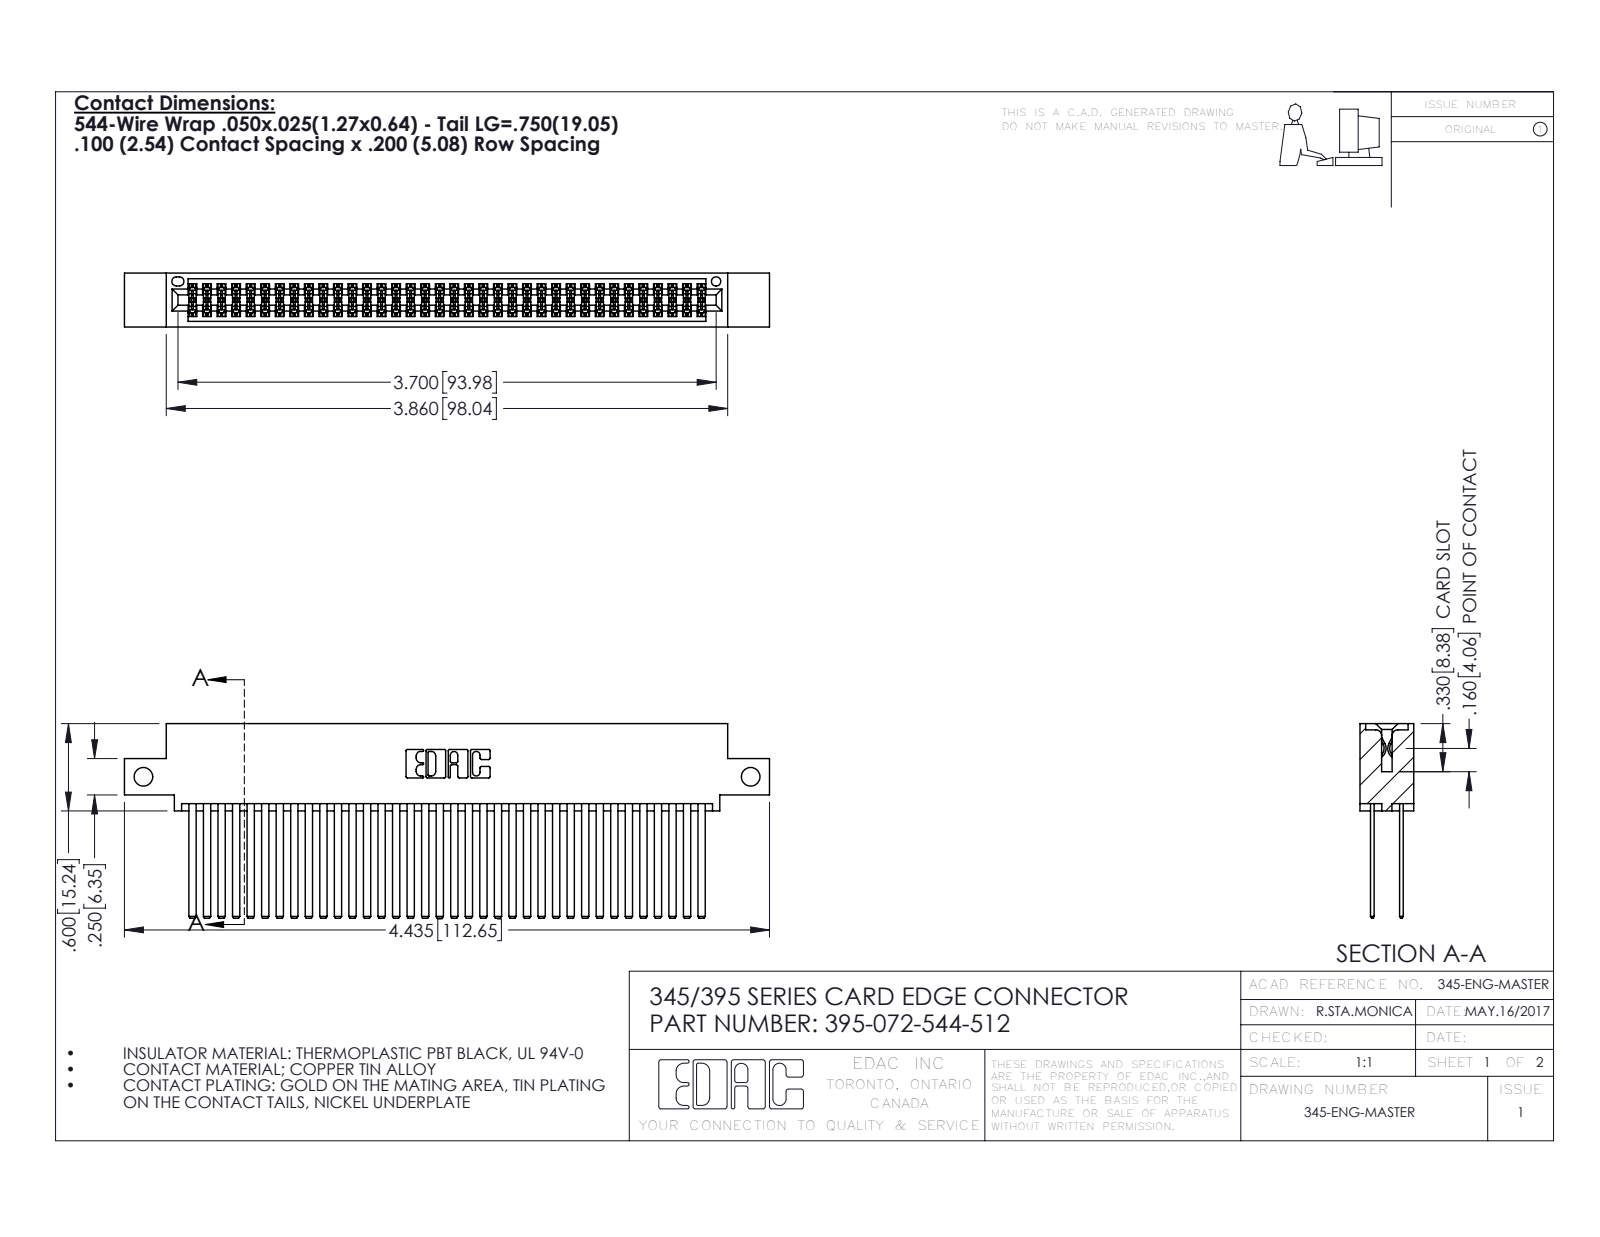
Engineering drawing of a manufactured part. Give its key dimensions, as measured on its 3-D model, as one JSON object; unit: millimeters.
{"part_name": "345 Part_0.110 Offset - Side Mount; 345-292-001_345-293-144; 395-072-544-512", "step_written_by": "SolidWorks 2016 (CONFIG_CONTROL_DESIGN)", "units": "millimeters", "bodies": {"solids": 73, "faces": 3298, "planar": 2172, "cylindrical": 1126, "other": 0}, "overall_size": [112.6, 34, 9.4], "volume_mm3": 11700, "surface_area_mm2": 20150, "round_holes": [[3.3, 2], [1.6, 1]], "partial_cylinders_radius": [[0.2, 108], [0.3, 22], [0.2, 6], [0.8, 6], [0.7, 3], [0.4, 2], [0.5, 2], [0.6, 2]], "face_to_face_distances": [5.1, 0.6, 7.6, 1.8, 2.5, 6.9, 5.7, 4.4, 9.4, 1.3], "hole_center_spacings": [106]}
